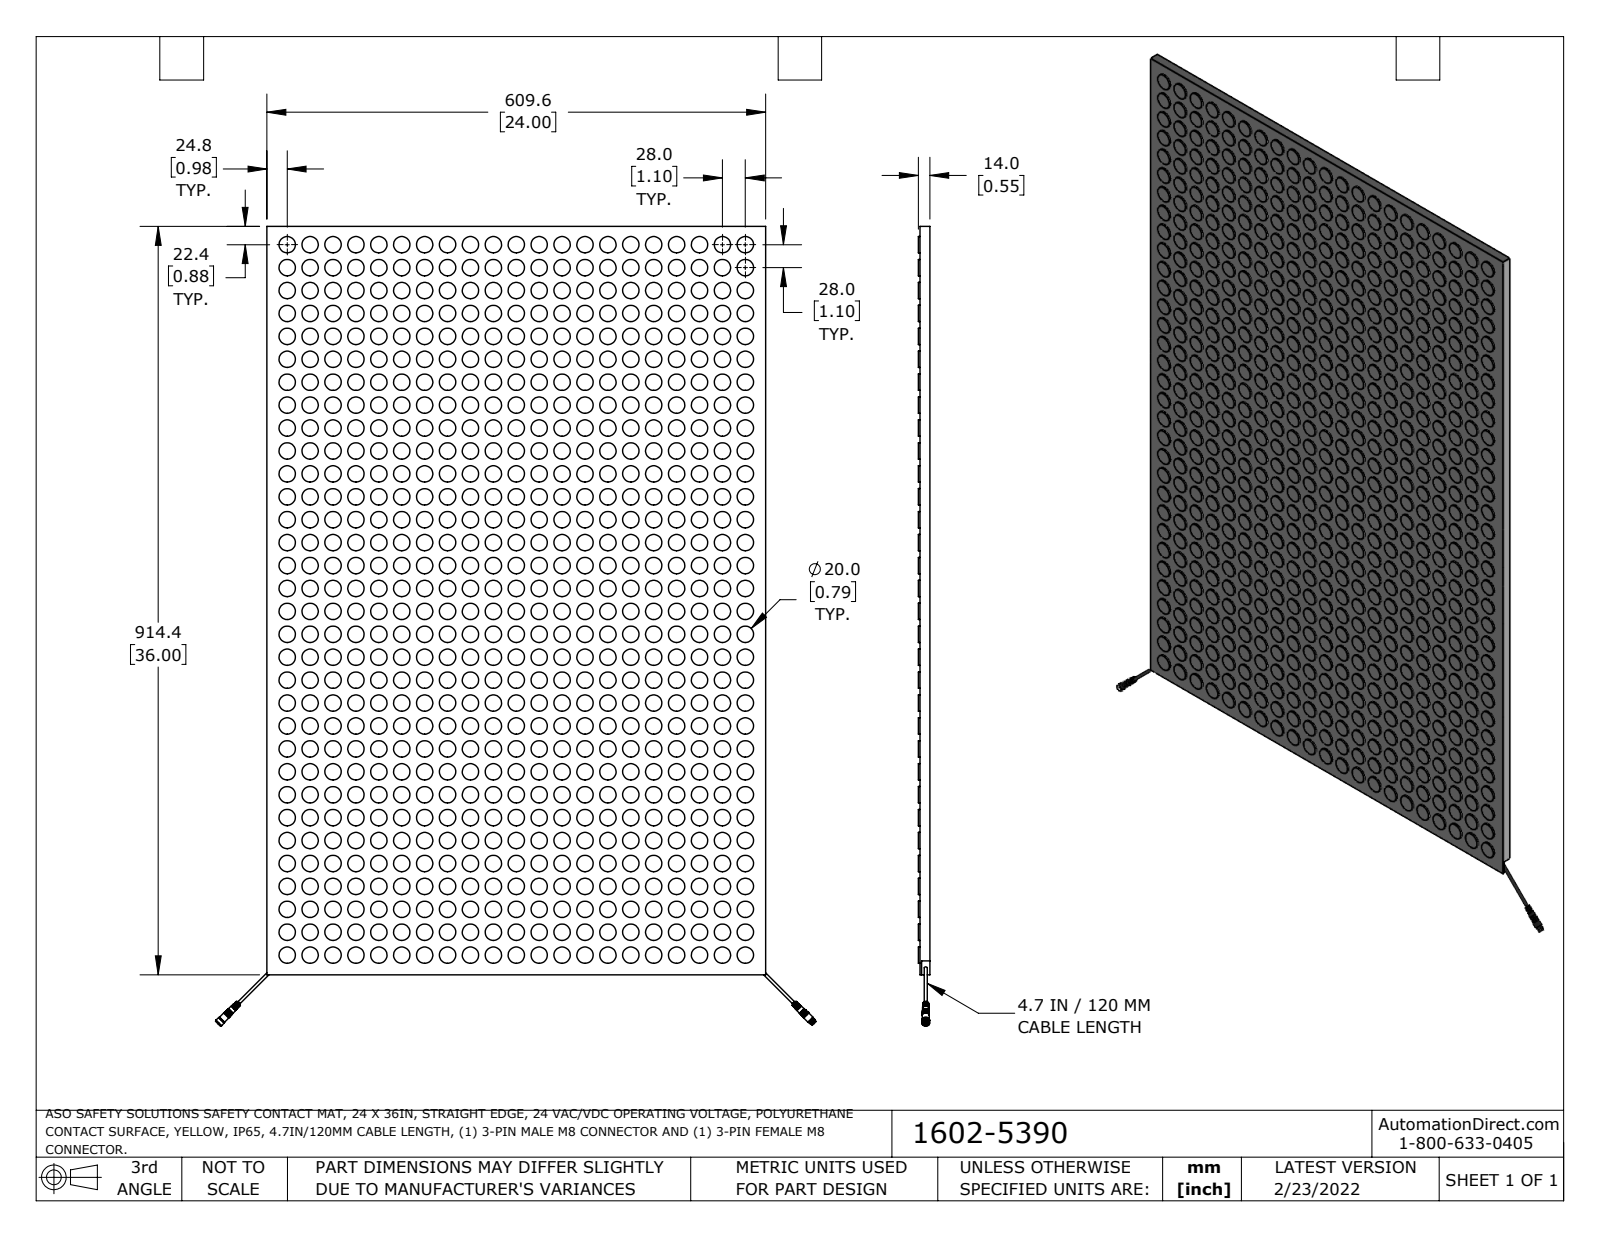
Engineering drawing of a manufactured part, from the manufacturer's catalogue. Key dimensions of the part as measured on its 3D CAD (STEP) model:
Part name (STEP PRODUCT): 1602-5390_Default
STEP written by: SolidWorks 2021 (CONFIG_CONTROL_DESIGN)
Units: inches
Bodies: 20 solids, 2400 faces (800 planar, 1462 cylindrical, 138 other)
Overall size (bounding box): 38.474 × 28.904 × 0.551
Volume: 434.1 in³ · Surface area: 1 924 in²
Round holes (diameter × count): ⌀0.063 ×3, ⌀0.134 ×2, ⌀0.228 ×1, ⌀0.232 ×1, ⌀0.272 ×1, ⌀0.283 ×1
Round bosses / shafts (diameter × count): ⌀0.787 ×672, ⌀0.047 ×24, ⌀0.031 ×8, ⌀0.039 ×3, ⌀0.346 ×2, ⌀0.138 ×2, ⌀0.378 ×1, ⌀0.354 ×1
Main face-to-face distances: 0.472, 0.079, 0.551, 24, 36, 0.157, 0.394, 0.087, 0.047, 0.173
Hole centre spacings: 0.069, 0.098, 0.138
